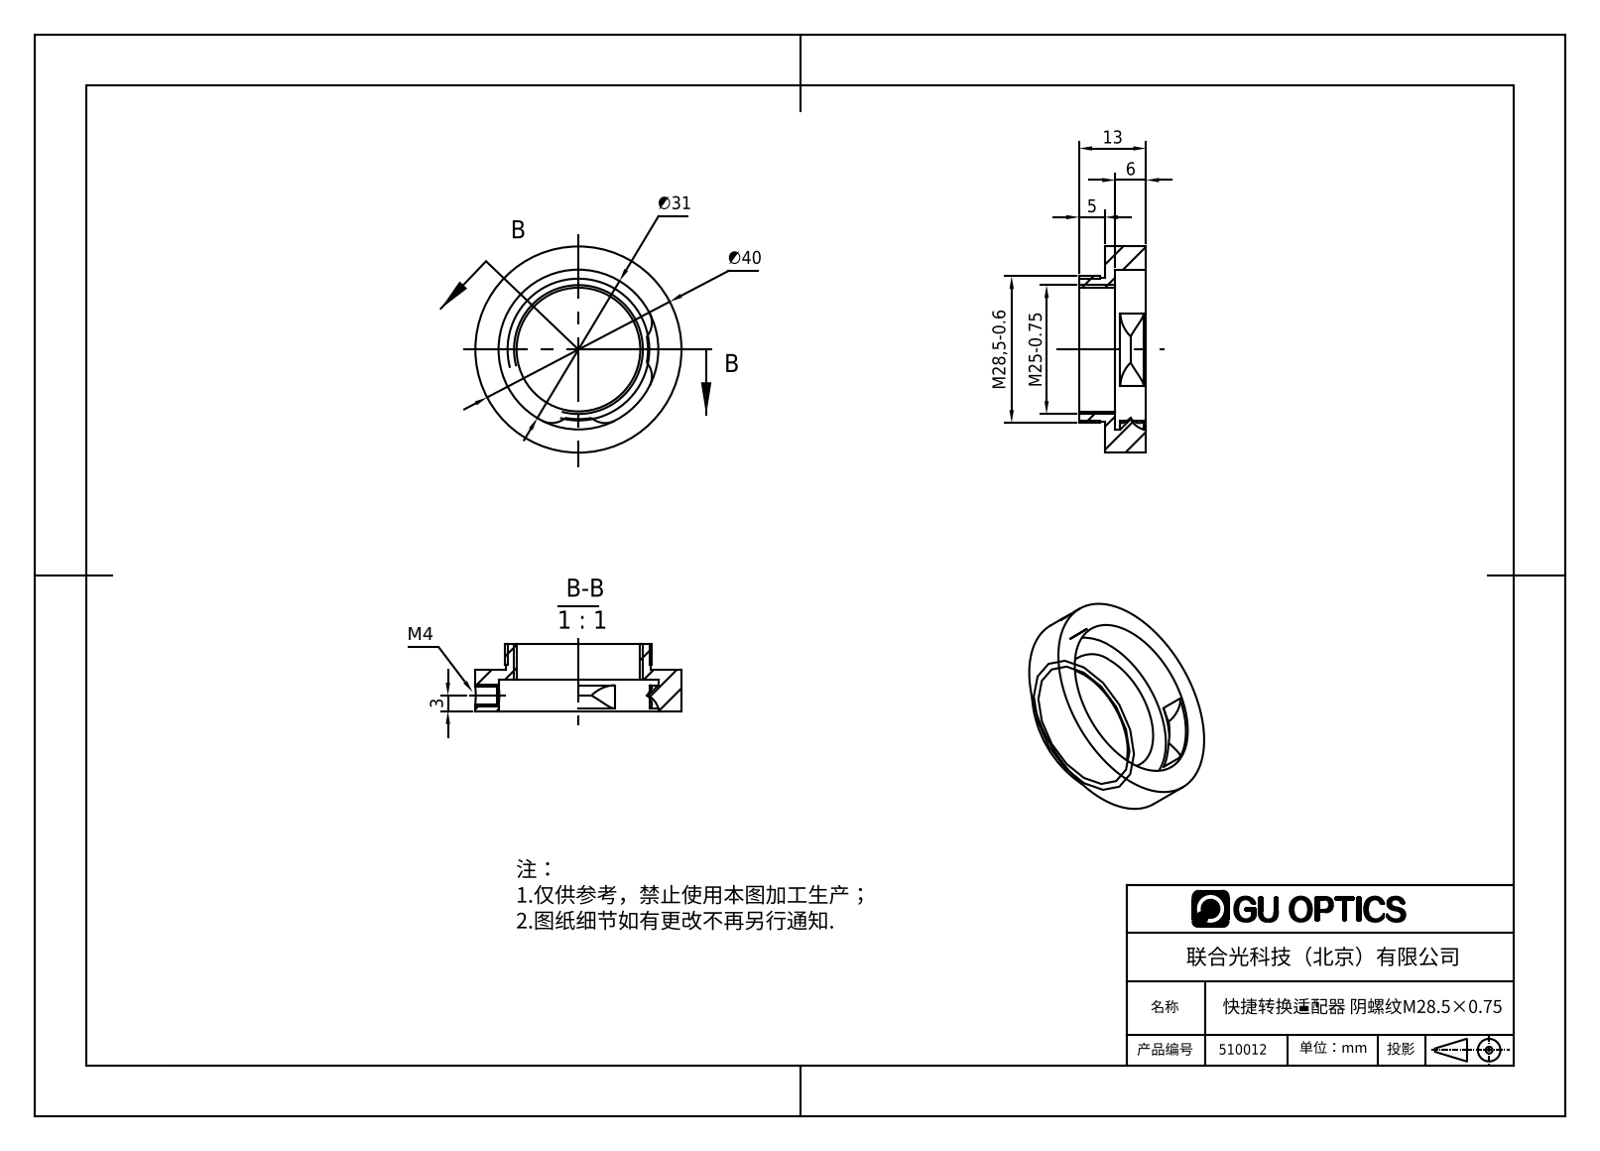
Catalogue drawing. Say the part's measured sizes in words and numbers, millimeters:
The part is named "510012". Its 3-D file was written by "SolidWorks 2016 (CONFIG_CONTROL_DESIGN)". It is 1 solid with 30 faces: 5 planar, 19 cylindrical and 6 other. Overall it measures 40 by 40 by 13 millimeters. Its volume is 5 558 cubic millimeters and its surface area 4 268 square millimeters. Round holes: 1 of diameter 3.3, 1 of diameter 4.05, 1 of diameter 24, 1 of diameter 31. Round bosses or shafts: 1 of diameter 40, 1 of diameter 28.5, 1 of diameter 28. Partial cylindrical surfaces (rounded edges, fillets, slot ends): 4 of radius 4. The main face-to-face distances are 8, 2, 6, 5, 7, 13, 4, 1, 3, 9.
